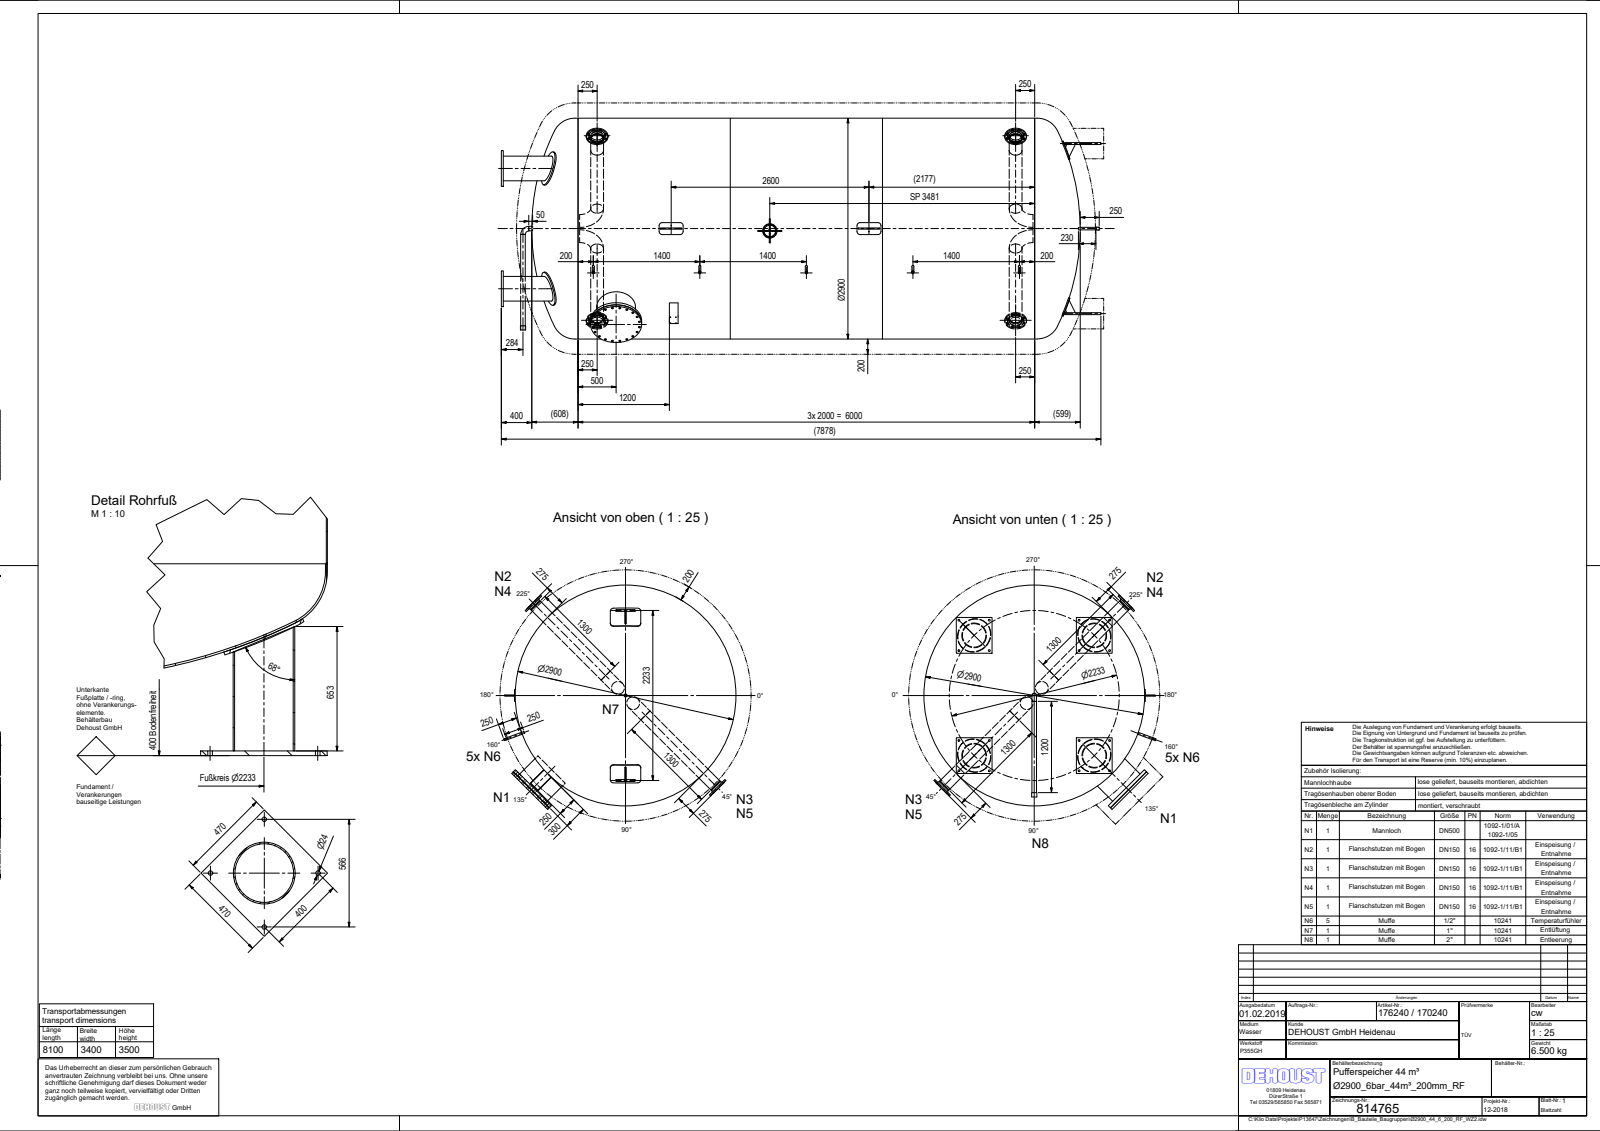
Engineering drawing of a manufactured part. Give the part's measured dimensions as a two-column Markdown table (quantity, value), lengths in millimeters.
| quantity | value |
| --- | --- |
| part name | Ø2900_44_6_200_RF_WZ2; Klöpper_Gew_Ø2900_8,3; Klöpper_Gew_Ø2900_10,3; Zyl_Ø2900_6x6000_2019 (+8 more) |
| STEP written by | Autodesk Inventor 2019 (AUTOMOTIVE_DESIGN) |
| units | millimeters |
| bodies | 58 solids, 449 faces (178 planar, 225 cylindrical, 46 other) |
| overall size | 7878.11 × 3051.99 × 2946.24 |
| volume | 748 000 000 mm³ |
| surface area | 165 300 000 mm² |
| round holes (diameter × count) | 26 × 36, 22 × 32, 24 × 16, 159.3 × 8, 18.63 × 5, 21.7 × 5, 26.9 × 5, 5.8 × 4, 168.3 × 4, 307.9 × 4, 5 × 2, 52.3 × 2 |
| round bosses / shafts (diameter × count) | 168.3 × 8, 26.9 × 5, 26.4 × 5, 450 × 4, 323.9 × 4, 285 × 4, 212 × 4, 2900 × 1 |
| partial cylindrical surfaces (radius × count) | 42 × 16, 10 × 6, 6 × 4, 5 × 2, 36 × 2, 72 × 2, 125 × 1, 1460 × 1 |
| main face-to-face distances | 25, 600, 3785.46, 4230.46, 3760.46, 4205.46, 445, 27.99, 2777.5, 3222.5 |
| hole center spacings | 120, 310, 191.59, 1400, 501.59, 5500, 169.71, 438.41 |
